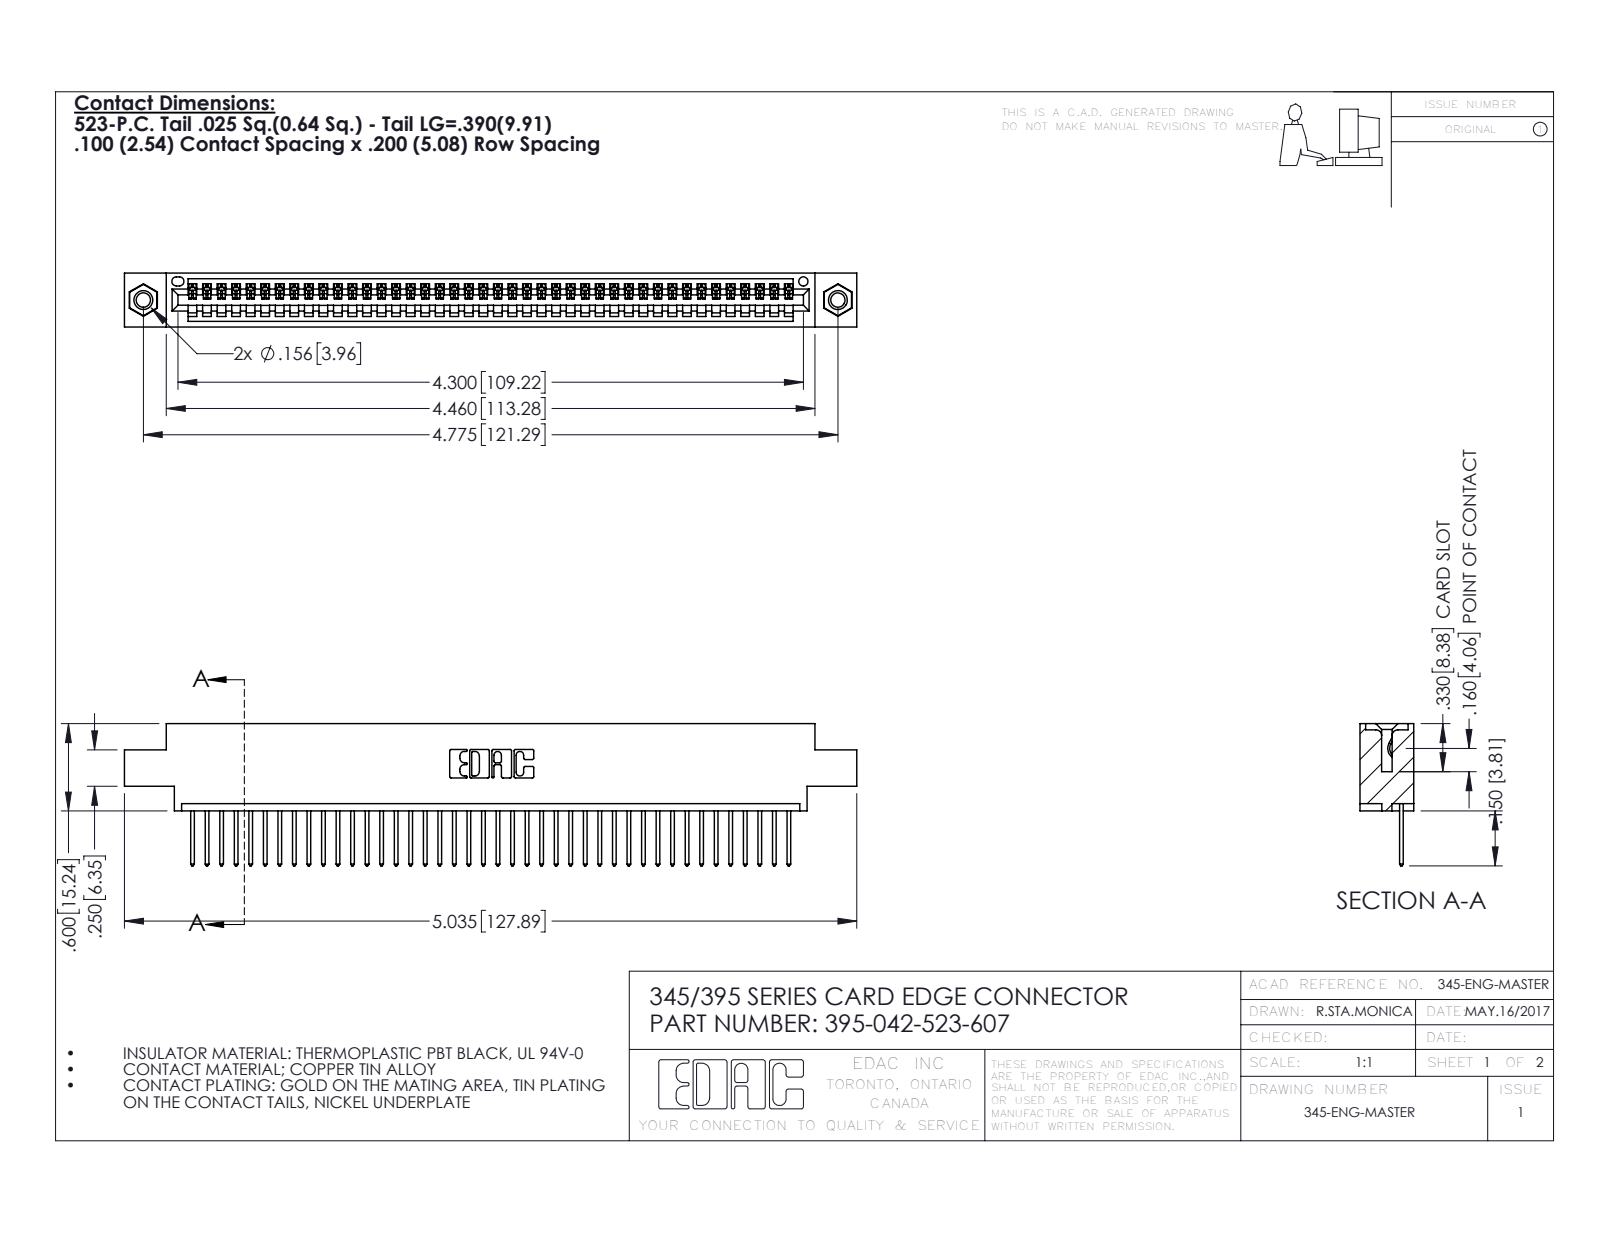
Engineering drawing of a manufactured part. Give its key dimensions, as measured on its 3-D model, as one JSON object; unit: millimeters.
{"part_name": "345-292-001_345-293-123; 345 Part_0.170 Offset - 0.156 Dia-TI; 395-042-523-607; 345-250-001_345-250-005-103", "step_written_by": "SolidWorks 2016 (CONFIG_CONTROL_DESIGN)", "units": "millimeters", "bodies": {"solids": 45, "faces": 2626, "planar": 1796, "cylindrical": 814, "other": 16}, "overall_size": [127.9, 24.8, 9.4], "volume_mm3": 12000, "surface_area_mm2": 16150, "round_holes": [[2.5, 2], [3.2, 2], [4, 2], [1.6, 1]], "round_bosses_or_shafts": [[3.9, 2]], "partial_cylinders_radius": [[0.2, 84], [0.3, 84], [0.3, 22], [0.2, 6], [0.8, 6], [0.7, 3], [0.8, 2], [1, 2]], "face_to_face_distances": [1.8, 7.6, 9.4, 5.1, 2.5, 6.9, 0.6, 5.7, 4.4, 3.8], "hole_center_spacings": [6.9, 115.3, 121.3]}
